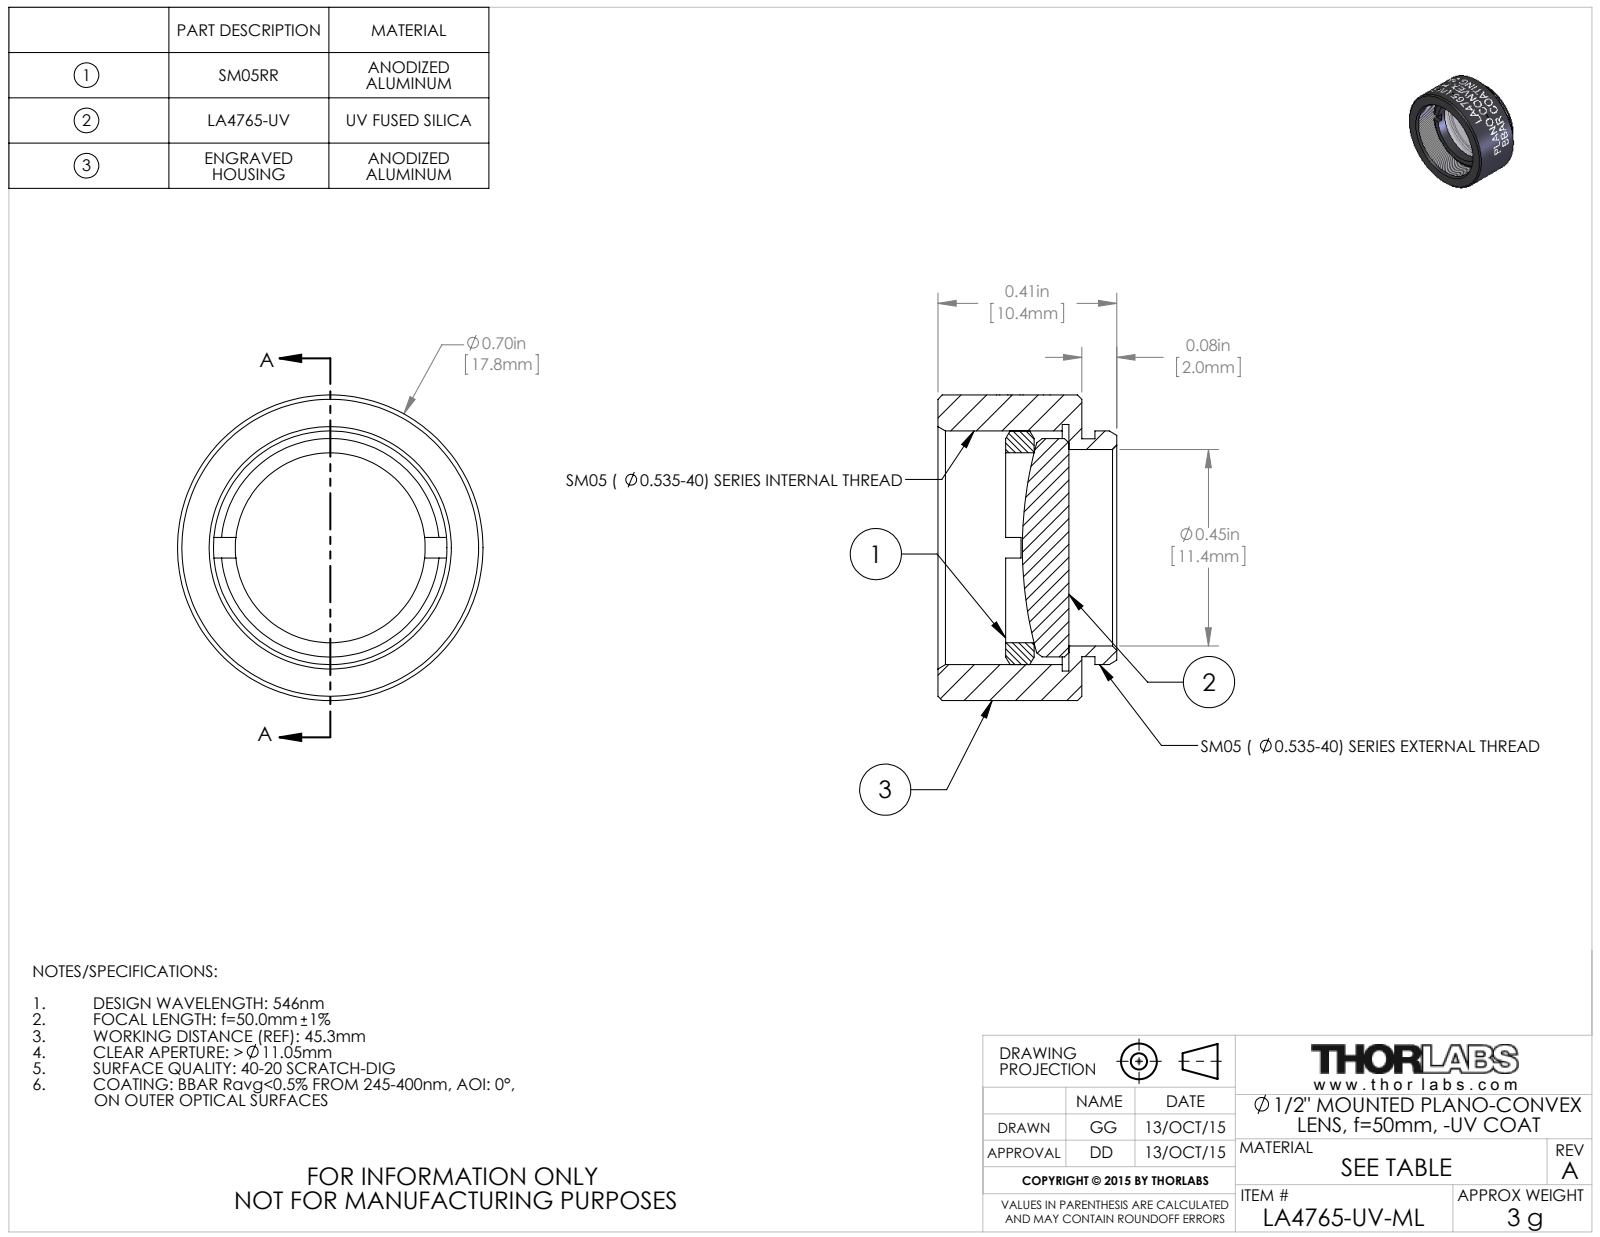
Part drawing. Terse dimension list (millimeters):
name: TTN039389-E0W
written by: SolidWorks 2014 (CONFIG_CONTROL_DESIGN)
unit: mm
bodies: 3 solids, 145 faces (16 planar, 108 cylindrical, 21 other)
size: 17.78 × 17.78 × 10.41
volume: 1 311 mm³; area: 1 832 mm²
holes: 1× ⌀11.05, 1× ⌀11.43, 1× ⌀13.59, 1× ⌀14.35
bosses: 1× ⌀17.78, 1× ⌀13.59, 1× ⌀12.7, 1× ⌀12.67
face distances: 0.76, 8.38, 7.62, 2.79, 2.03, 5.59, 4.44, 3.68, 1.65, 3.94
